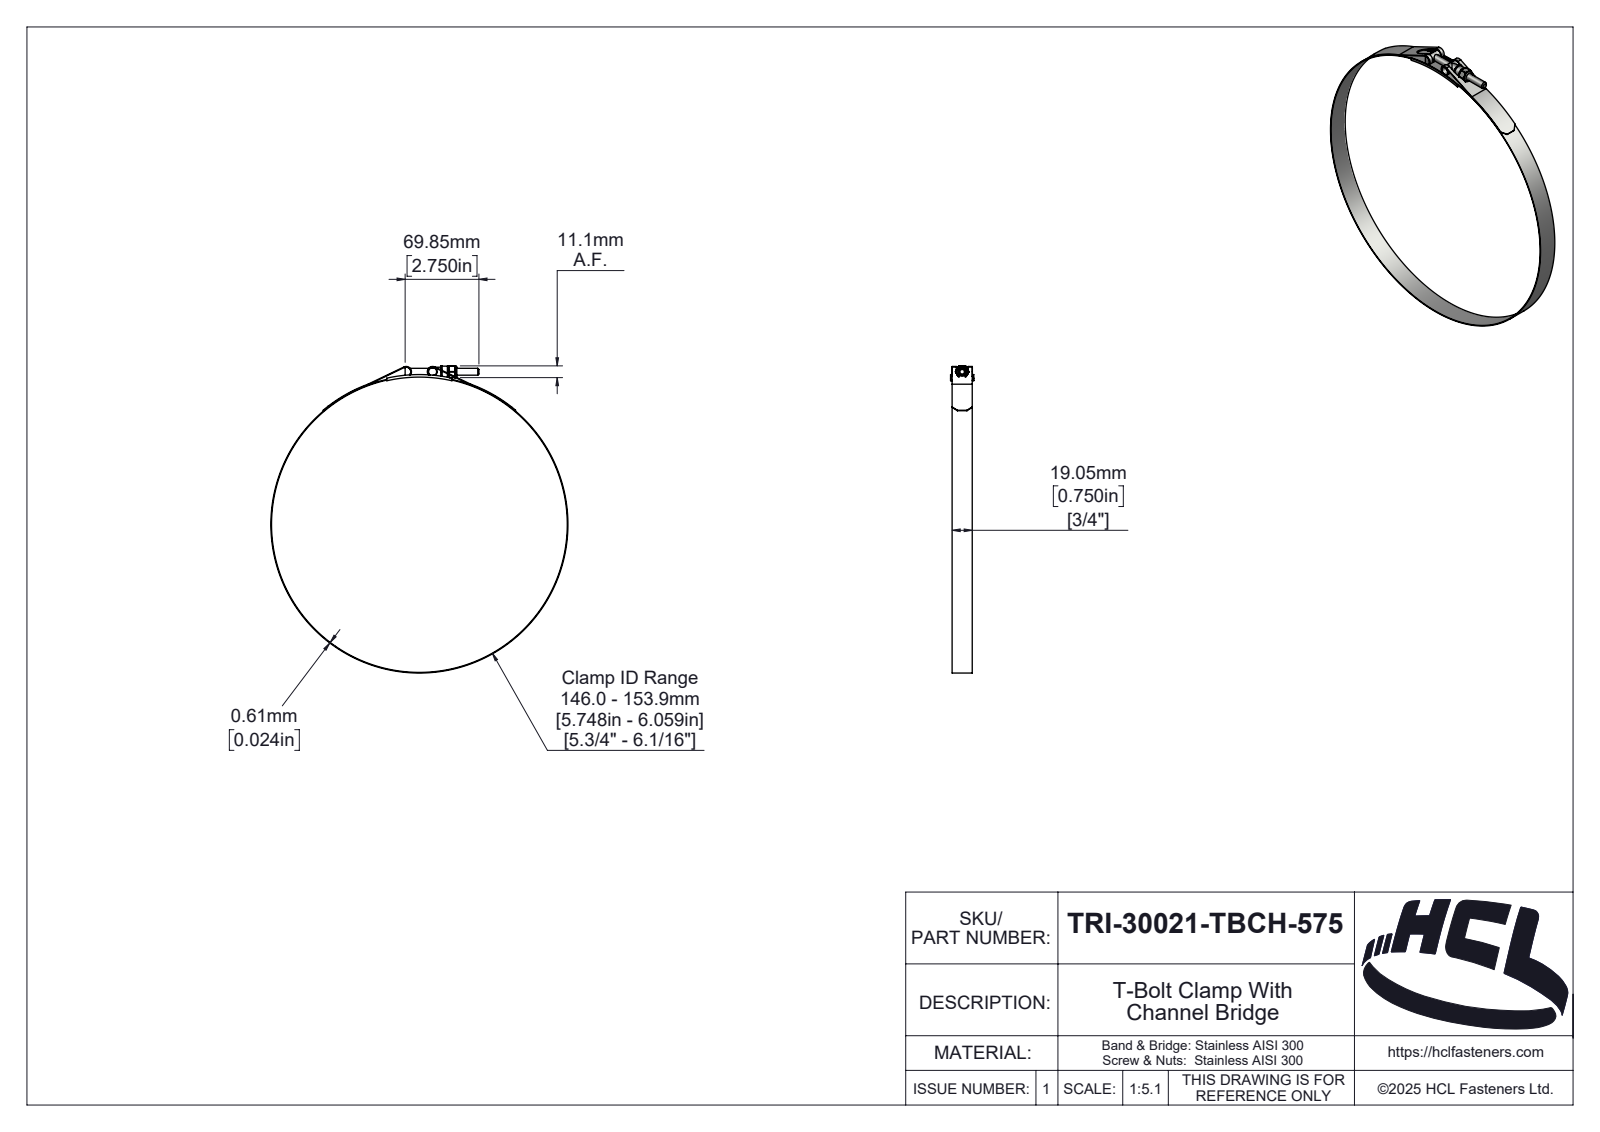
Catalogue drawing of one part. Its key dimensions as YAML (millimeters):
part_name: "TRI-30021-TBCH-575"
step_written_by: "SolidWorks 2025 (AUTOMOTIVE_DESIGN)"
units: millimeters
bodies: {solids: 6, faces: 330, planar: 46, cylindrical: 122, other: 162}
overall_size: [290.79, 281.22, 22]
volume: 17064
surface_area: 48086
round_holes:
  - {diameter: 5.4, count: 1}
  - {diameter: 6.35, count: 1}
  - {diameter: 6.5, count: 1}
  - {diameter: 7.58, count: 1}
  - {diameter: 280, count: 1}
round_bosses_or_shafts:
  - {diameter: 8.58, count: 2}
  - {diameter: 281.22, count: 1}
  - {diameter: 10.58, count: 1}
partial_cylinders:
  - {radius: 0.39, count: 6}
  - {radius: 0.5, count: 2}
  - {radius: 4.39, count: 2}
  - {radius: 5, count: 2}
  - {radius: 0.59, count: 1}
  - {radius: 2.42, count: 1}
  - {radius: 3.03, count: 1}
  - {radius: 3.19, count: 1}
face_to_face_distances: [0.61, 19.06, 1.47, 20.53, 21.39, 0.86, 19.92, 0.74, 22, 20.78]
hole_center_spacings: [145]
